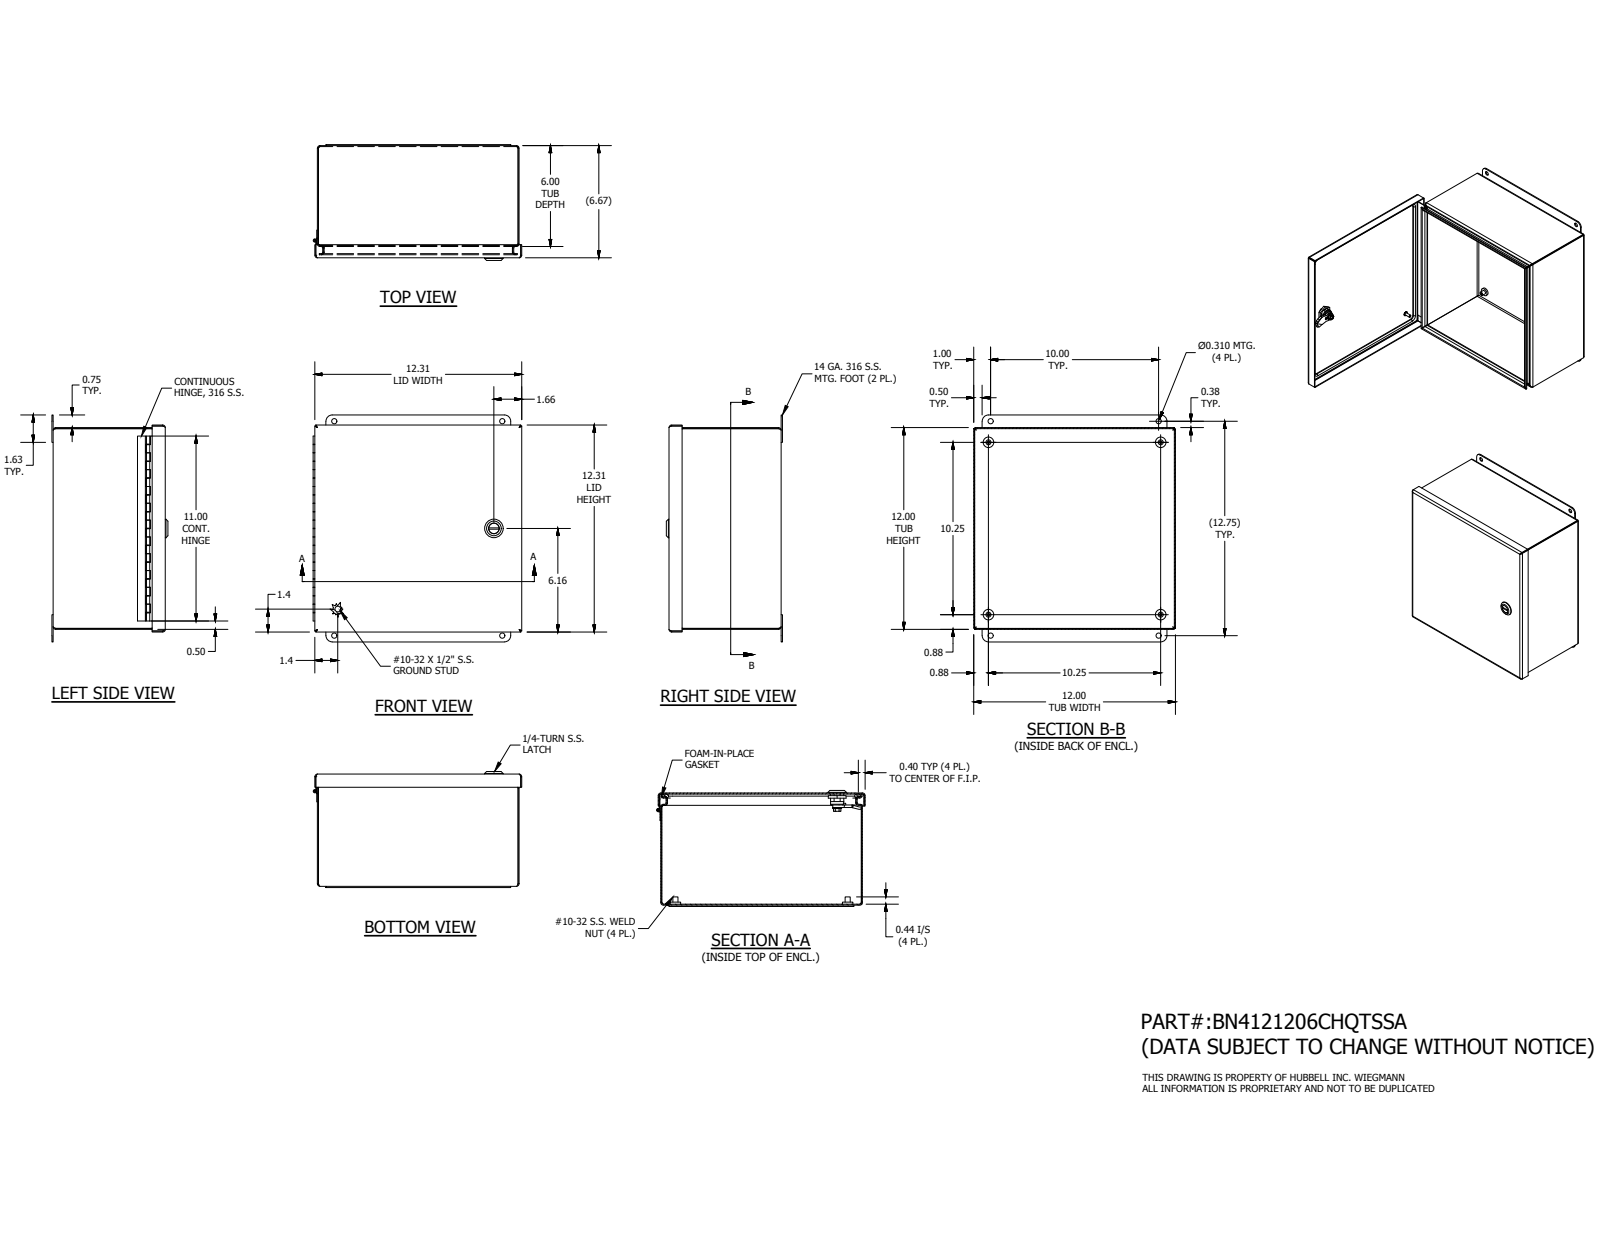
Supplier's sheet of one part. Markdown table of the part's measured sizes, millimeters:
| quantity | value |
| --- | --- |
| part name | BN41212CHQTSSALID; 12x12; 348131; 32884LH (+8 more) |
| STEP written by | Autodesk Inventor 2016 (AUTOMOTIVE_DESIGN) |
| units | millimeters |
| bodies | 21 solids, 671 faces (366 planar, 208 cylindrical, 97 other) |
| overall size | 342.9 × 315.26 × 175.39 |
| volume | 768 268 mm³ |
| surface area | 964 559 mm² |
| round holes (diameter × count) | 3.96 × 4, 7.87 × 4, 2.96 × 1, 5 × 1, 8 × 1, 10 × 1, 10.2 × 1, 16.1 × 1, 20.38 × 1 |
| round bosses / shafts (diameter × count) | 15.88 × 4, 7.62 × 4, 28 × 1, 19.8 × 1, 16 × 1, 15.2 × 1, 13.5 × 1, 12.8 × 1 |
| partial cylindrical surfaces (radius × count) | 2.38 × 20, 3.88 × 20, 3.17 × 16, 0.5 × 8, 4 × 4, 9.53 × 4, 2.31 × 2, 6.45 × 1 |
| main face-to-face distances | 1.5, 1.49, 303.3, 167.99, 169.48, 166.49, 167.98, 304.8, 303.31, 301.81 |
| hole center spacings | 31.91, 260.35, 292.12, 389.18, 131.14, 254, 259.12, 259.13 |
